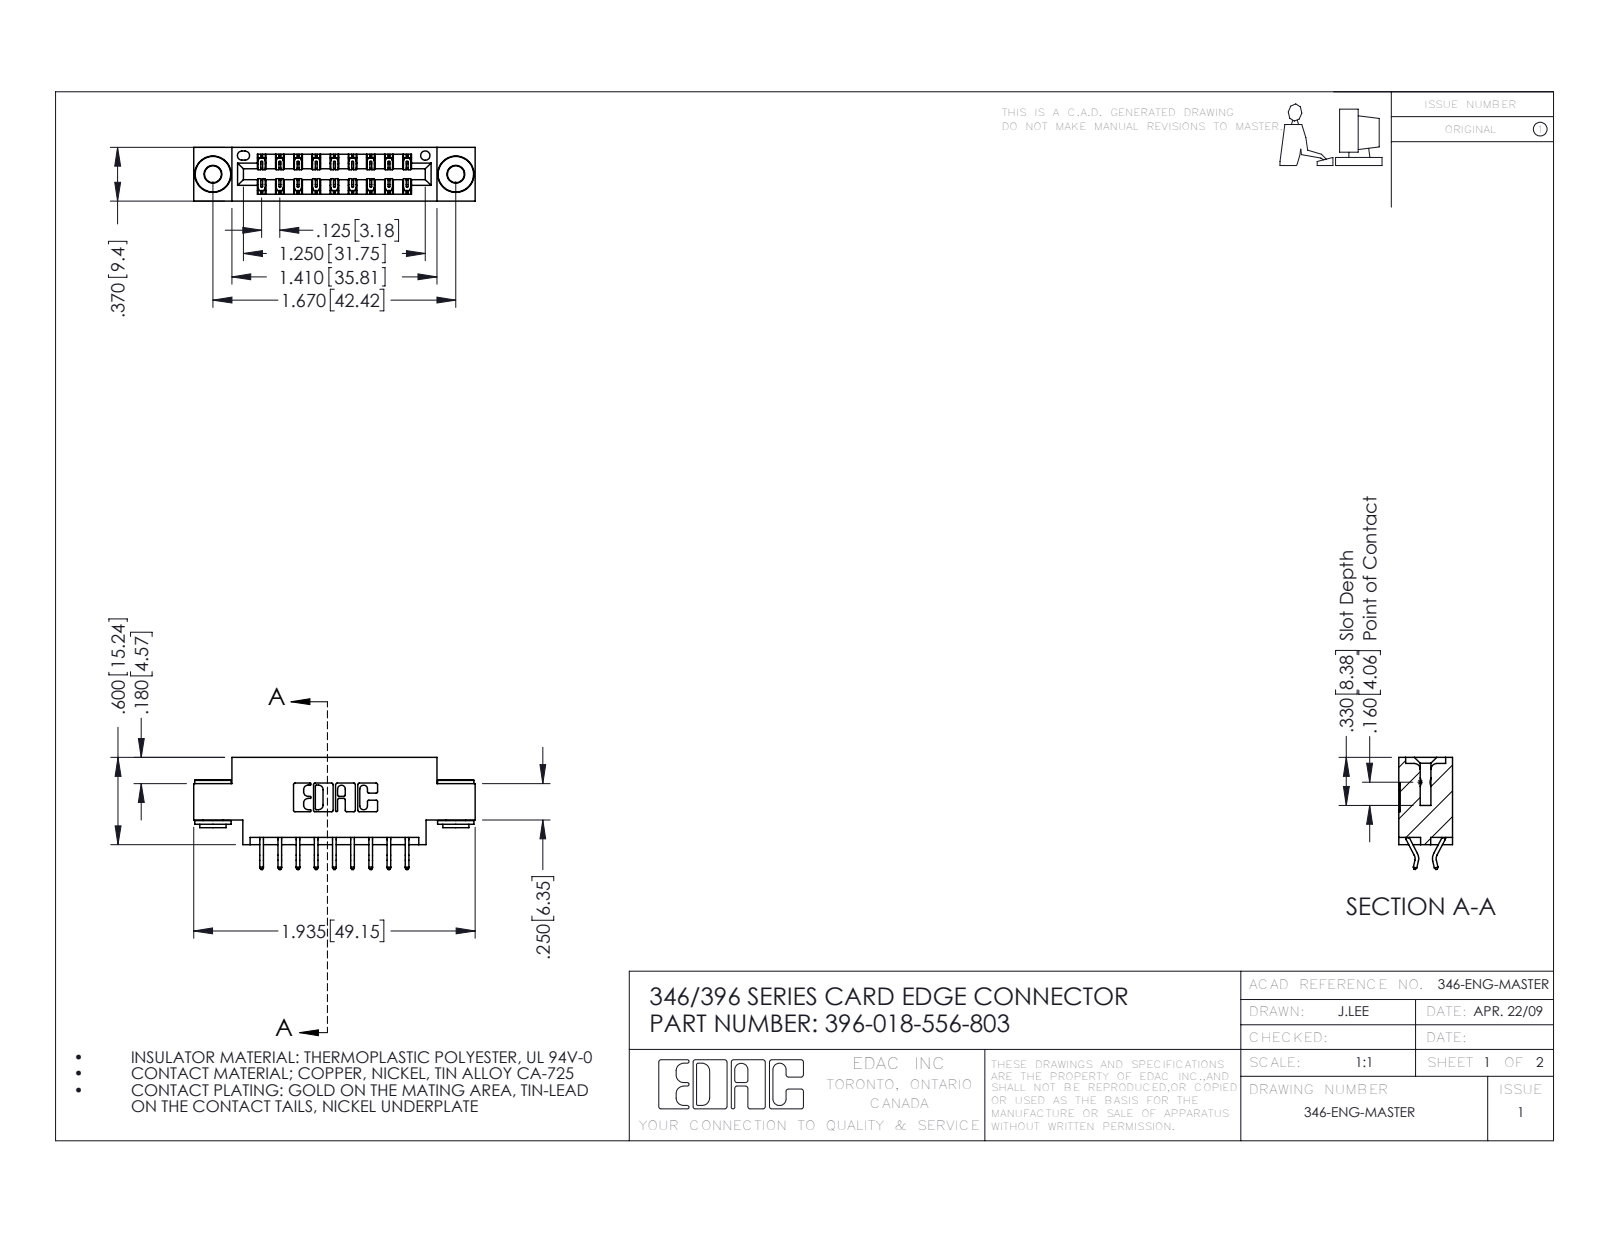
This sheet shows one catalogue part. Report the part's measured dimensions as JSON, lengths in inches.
{"part_name": "345-292-001_556 Tail; 346 Part_0.170 Offset - 0.156 Dia-TH; 345-250-002_345-250-002-102; 396-018-556-803", "step_written_by": "SolidWorks 2016 (CONFIG_CONTROL_DESIGN)", "units": "inches", "bodies": {"solids": 21, "faces": 1208, "planar": 792, "cylindrical": 408, "other": 8}, "overall_size": [1.935, 0.77, 0.37], "volume_in3": 0.269, "surface_area_in2": 9.156, "round_holes": [[0.116, 2], [0.156, 2], [0.064, 1]], "round_bosses_or_shafts": [[0.25, 2], [0.18, 2], [0.136, 2]], "partial_cylinders_radius": [[0.006, 27], [0.01, 22], [0.007, 6], [0.031, 6], [0.026, 3], [0.01, 2], [0.014, 2], [0.022, 2]], "face_to_face_distances": [0.25, 0.37, 0.048, 0.322, 0.025, 0.275, 0.148, 0.222, 0.1, 0.174], "hole_center_spacings": [0.246, 1.465, 1.67]}
